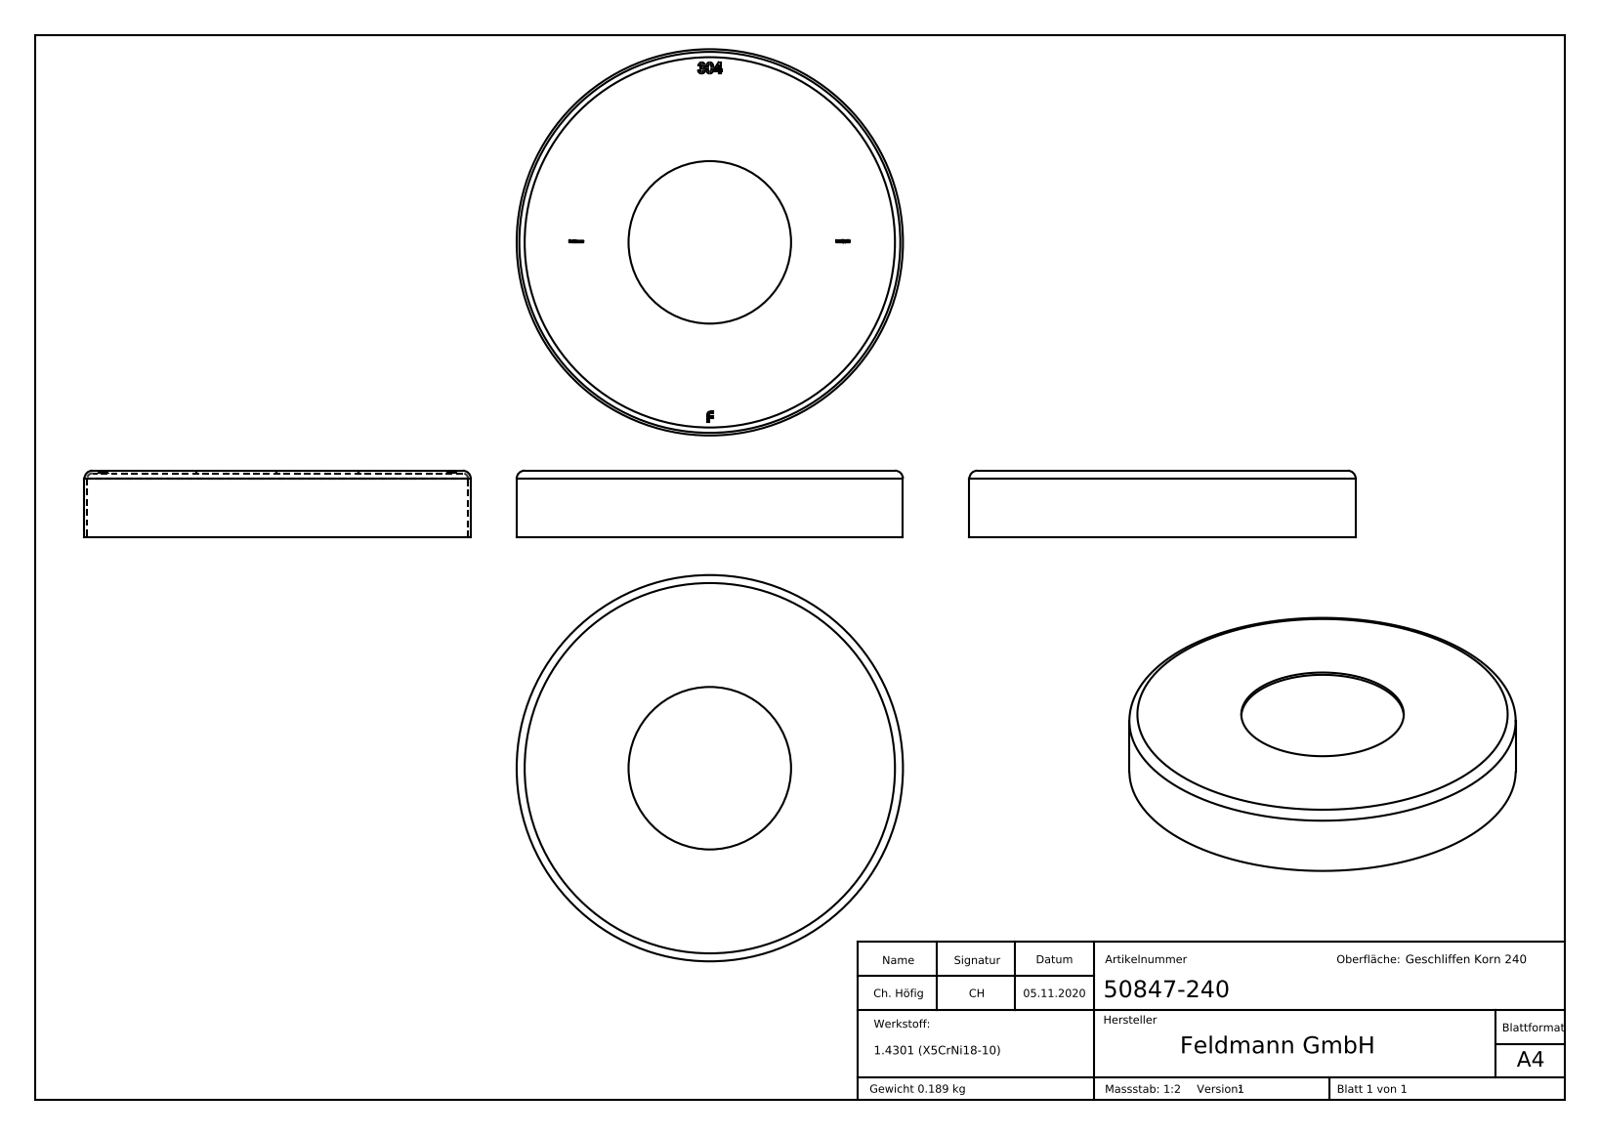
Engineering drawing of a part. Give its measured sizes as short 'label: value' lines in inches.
name: 50847-240
written by: SolidWorks 2018 (CONFIG_CONTROL_DESIGN)
unit: in
bodies: 1 solid, 296 faces (164 planar, 6 cylindrical, 126 other)
size: 5.709 × 5.709 × 0.984
volume: 1.462 in³; area: 75.29 in²
holes: 1× ⌀2.402, 1× ⌀5.63
bosses: 1× ⌀5.709
face distances: 0.039, 0.945, 0.984, 0.949, 0.035, 0.028, 0.197, 0.169, 0.023, 0.027
